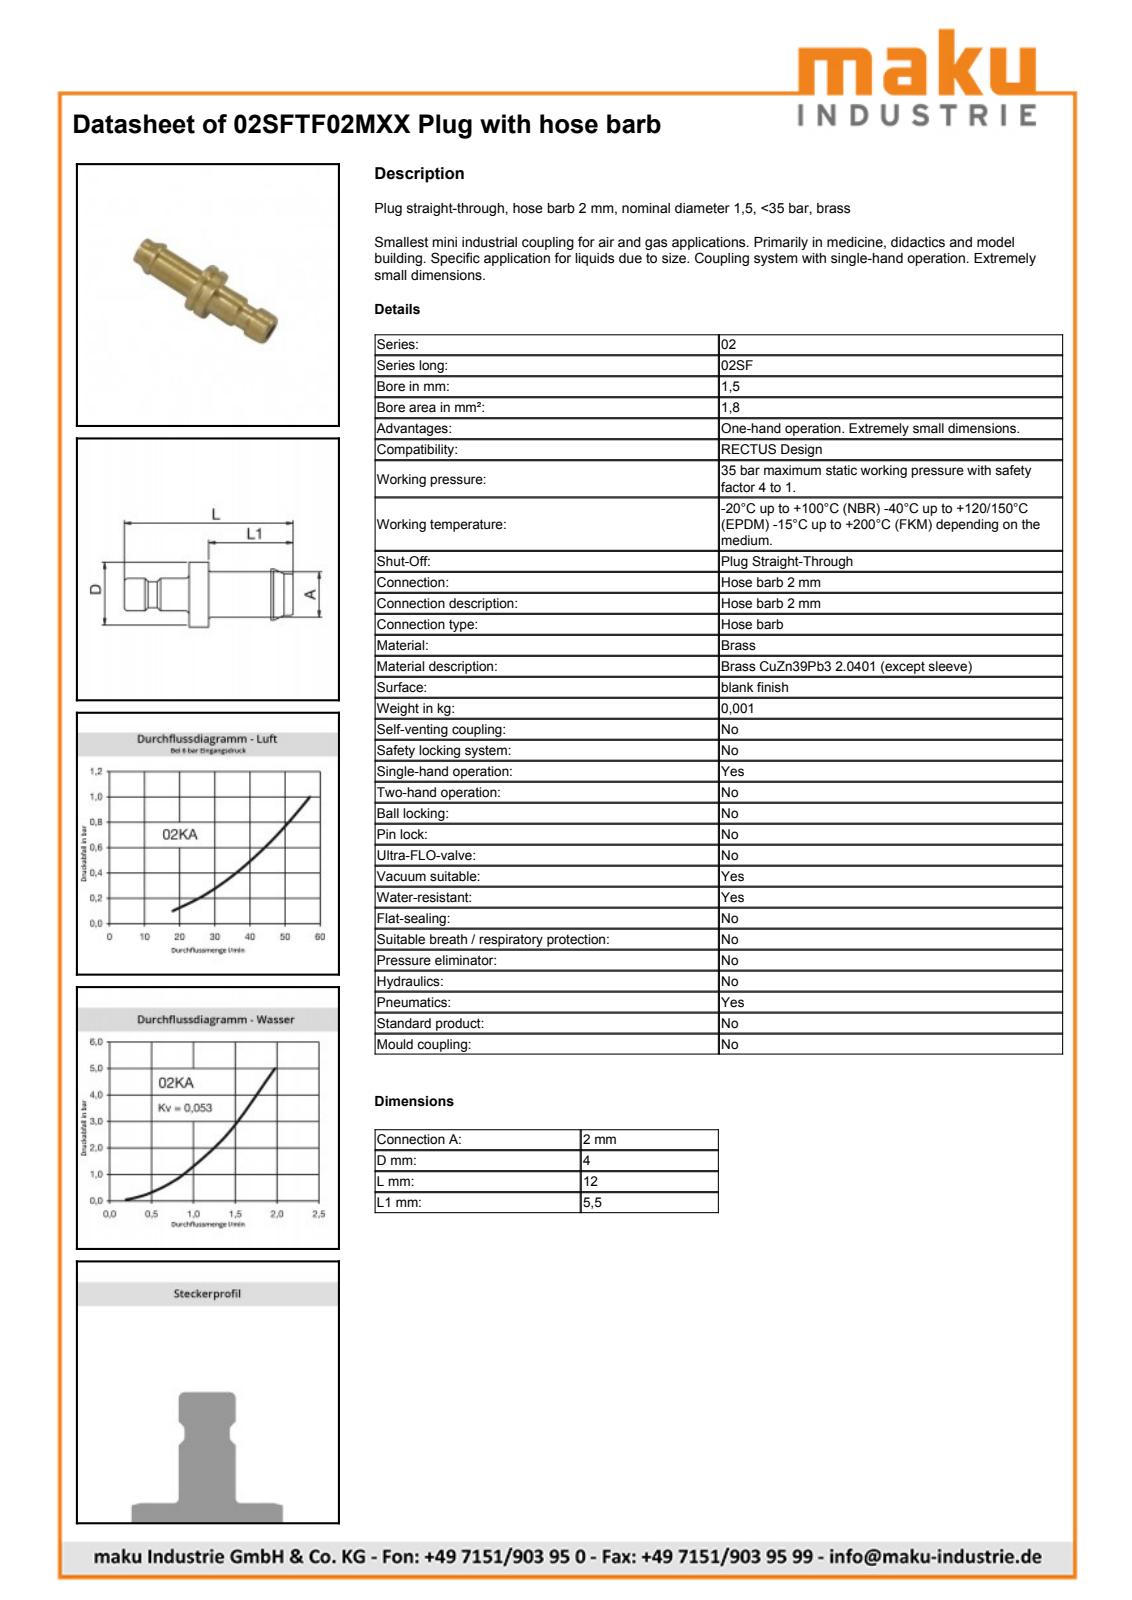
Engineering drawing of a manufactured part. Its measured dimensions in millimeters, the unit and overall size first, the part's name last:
Units: millimetres
Overall size (bounding box): 12 × 5 × 5
Round holes (diameter × count): ⌀1.5 ×1
Round bosses / shafts (diameter × count): ⌀5 ×1, ⌀2.95 ×1, ⌀2.54 ×1, ⌀2.5 ×1, ⌀2.2 ×1, ⌀2 ×1
Main face-to-face distances: 1.5, 5, 6.5, 10.3, 5.3, 3.8, 12, 7, 5.5, 1.7
Volume: 58 mm³ · Surface area: 199 mm²
Bodies: 1 solid, 25 faces (5 planar, 9 cylindrical, 11 other)
Part name (STEP PRODUCT): D107875
STEP written by: Autodesk Inventor 2013 (AUTOMOTIVE_DESIGN)
